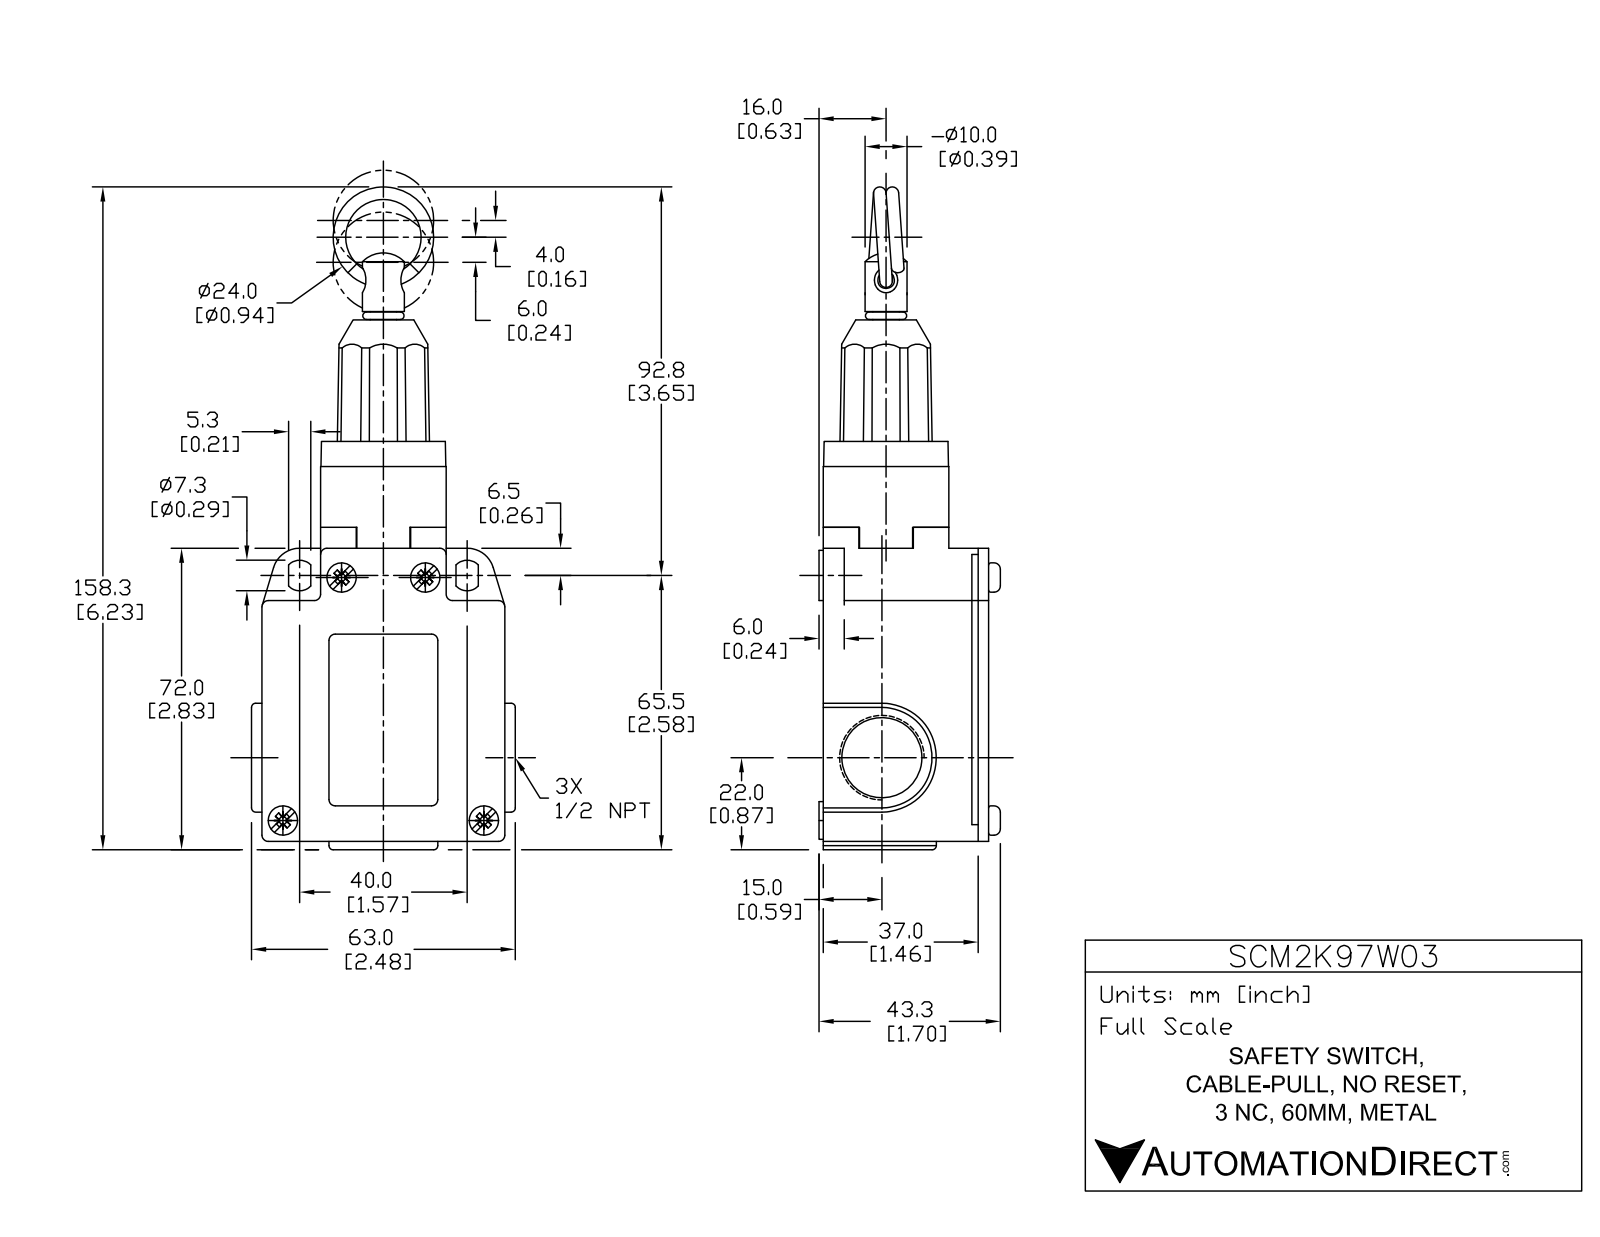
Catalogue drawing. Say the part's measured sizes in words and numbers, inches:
The part is named "SCM2K97W03". Its 3-D file was written by "SolidWorks 2017 (AUTOMOTIVE_DESIGN)". It is 5 solids with 202 faces: 89 planar, 88 cylindrical and 25 other. Overall it measures 6.28 by 2.441 by 1.705 inches. Its volume is 10.97 cubic inches and its surface area 48.85 square inches. Round holes: 2 of diameter 0.669, 2 of diameter 0.748, 1 of diameter 0.157, 1 of diameter 0.398, 1 of diameter 0.709. Round bosses or shafts: 4 of diameter 0.276, 2 of diameter 0.472, 2 of diameter 0.354, 1 of diameter 0.701, 1 of diameter 0.394, 1 of diameter 0.248. Partial cylindrical surfaces (rounded edges, fillets, slot ends): 12 of radius 0.059, 2 of radius 0.144, 2 of radius 0.256, 2 of radius 0.512, 1 of radius 0.453, 1 of radius 0.472. The main face-to-face distances are 1.555, 0.551, 1.732, 1.181, 2.283, 0.079, 0.236, 0.157, 0.197, 2.756. The hole center spacings are 0.039, 4.528.
